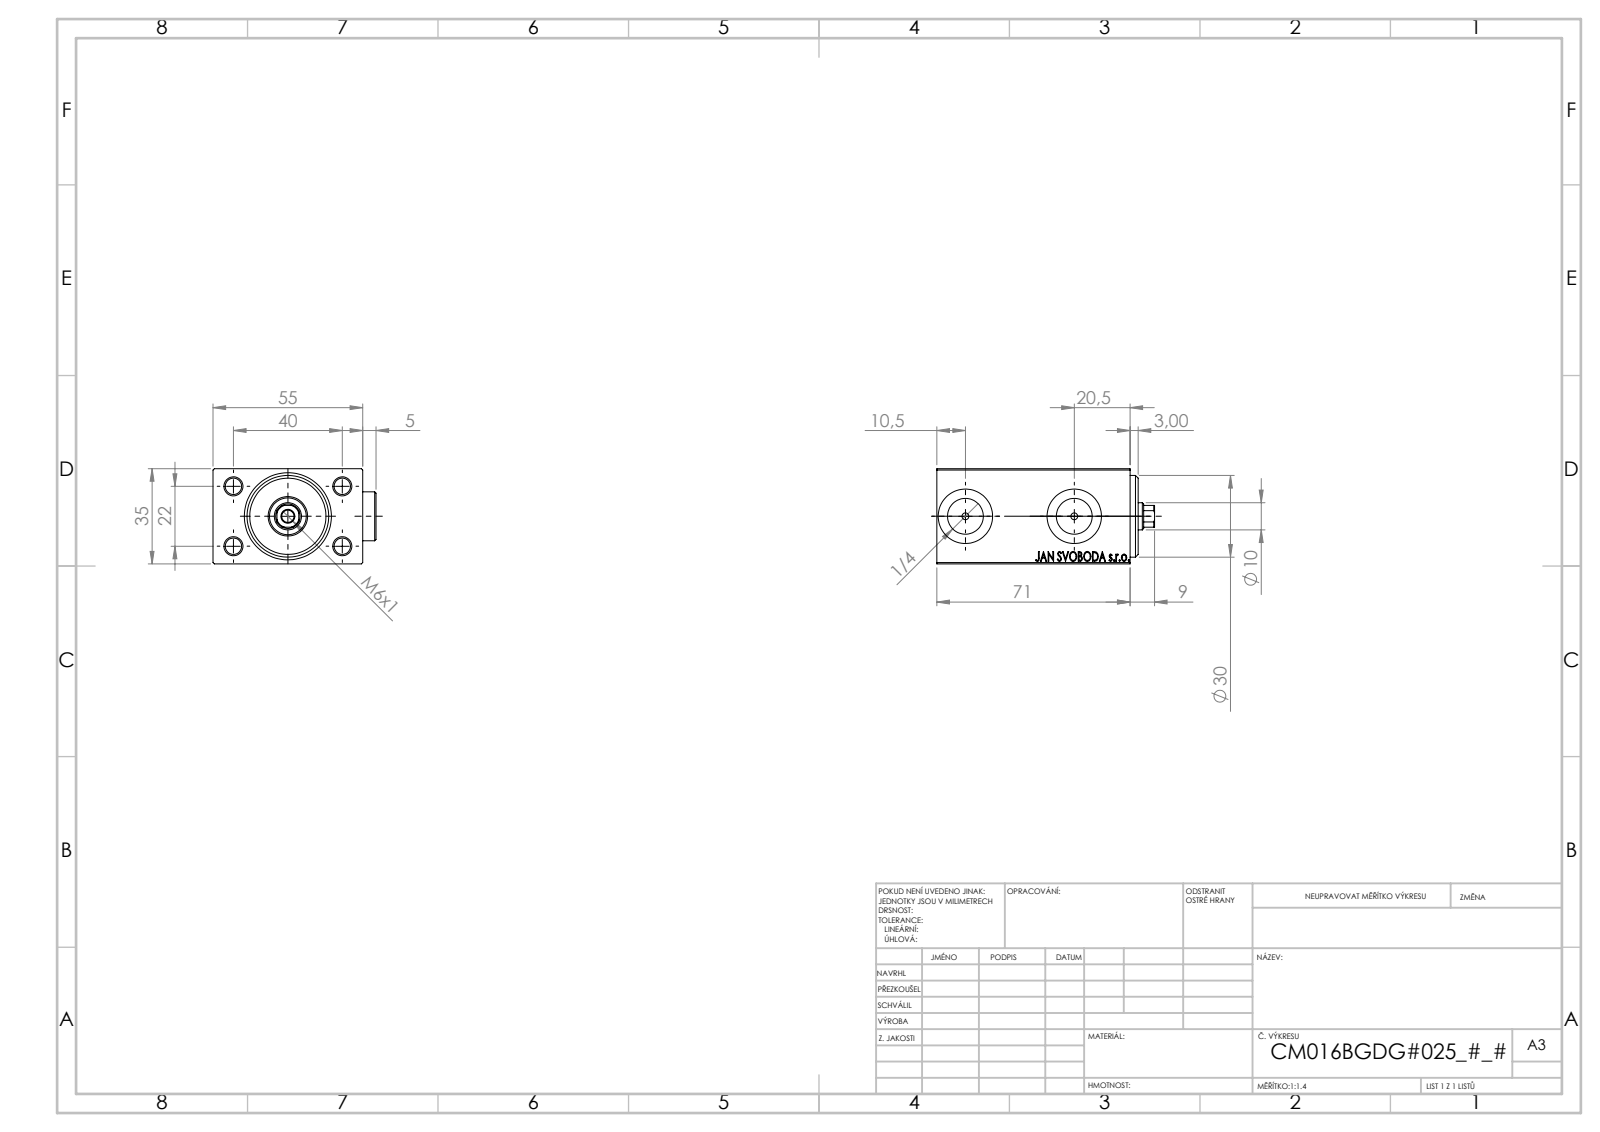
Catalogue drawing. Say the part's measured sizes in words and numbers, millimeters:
The part is named "V450CM_B_Body; V450CM_VC_B; V450CM_B_VCP". Its 3-D file was written by "SolidWorks 2019 (CONFIG_CONTROL_DESIGN)". It is 3 solids with 895 faces: 405 planar, 64 cylindrical and 426 other. Overall it measures 80 by 55 by 35 millimeters. Its volume is 125 838 cubic millimeters and its surface area 28 242 square millimeters. Round holes: 4 of diameter 6, 2 of diameter 2.5, 2 of diameter 13.16, 2 of diameter 20, 1 of diameter 4.5, 1 of diameter 10, 1 of diameter 13.5, 1 of diameter 14.5, 1 of diameter 16, 1 of diameter 18, 1 of diameter 30. Partial cylindrical surfaces (rounded edges, fillets, slot ends): 1 of radius 4.5. The main face-to-face distances are 35, 55, 5, 71, 66, 54.9, 13, 8, 3, 74. The hole center spacings are 22.83, 40, 22, 45.65.
